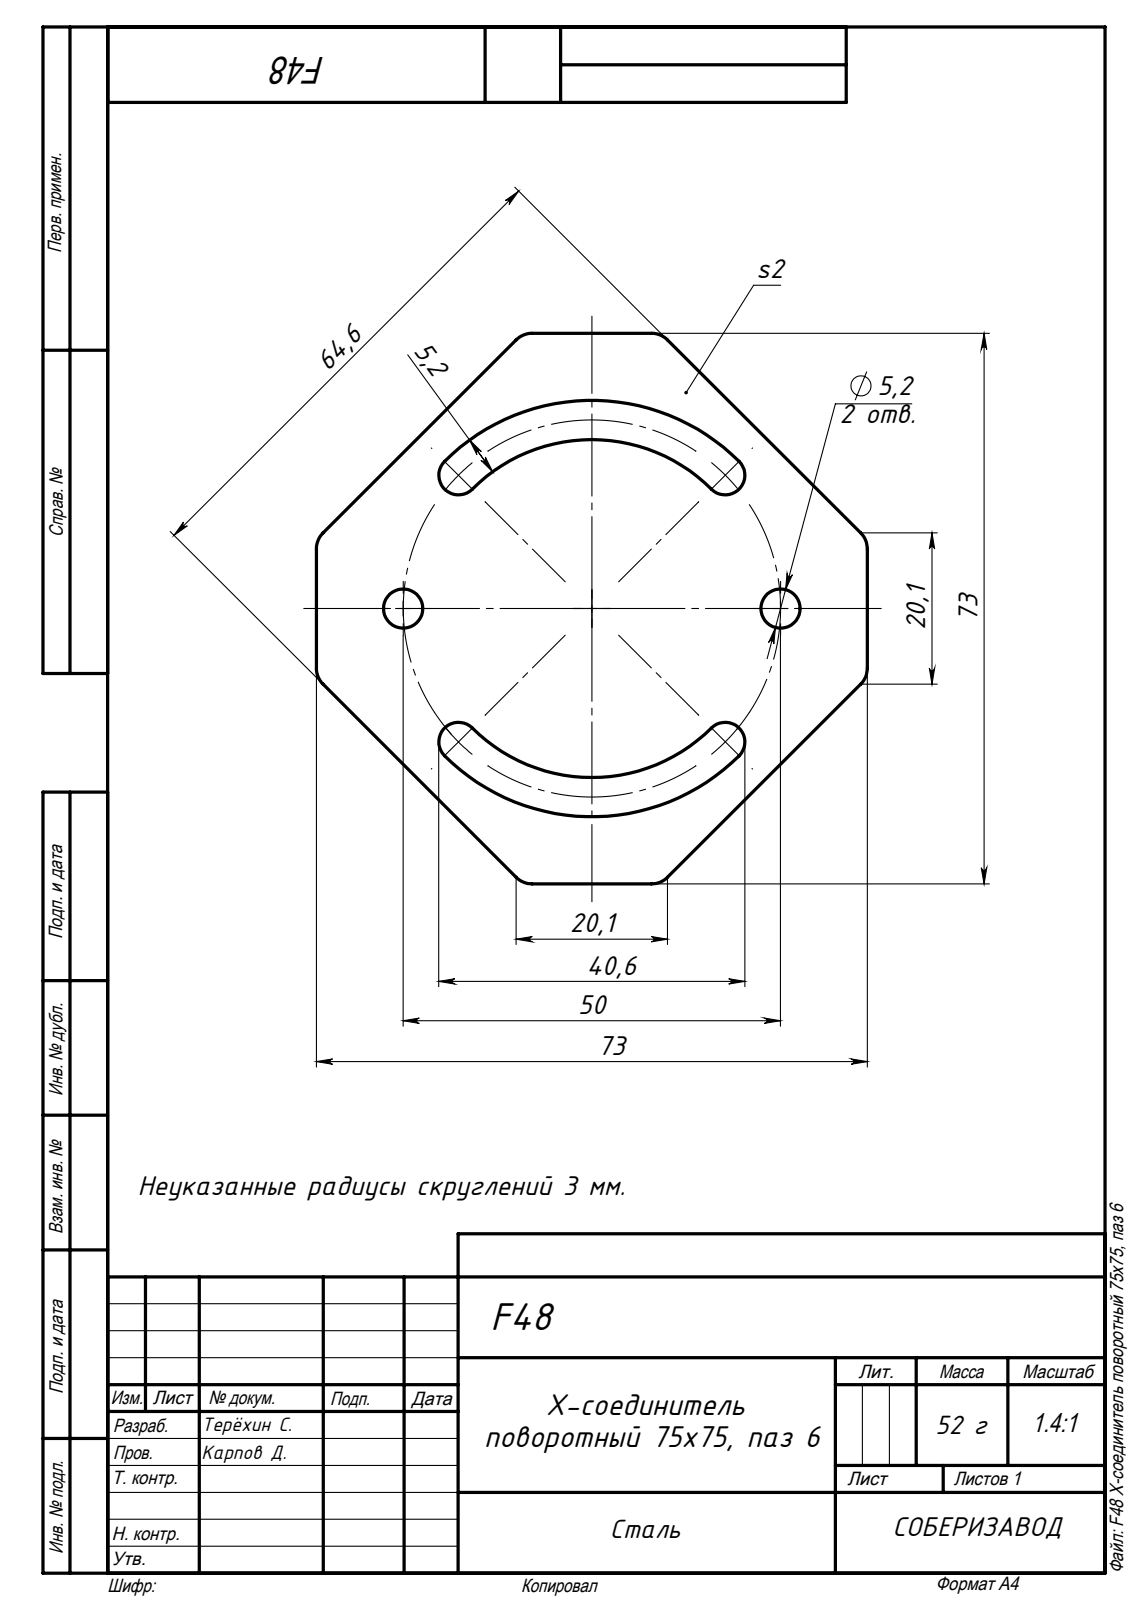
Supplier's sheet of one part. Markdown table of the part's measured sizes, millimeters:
| quantity | value |
| --- | --- |
| STEP written by | SolidWorks 2020 (AUTOMOTIVE_DESIGN) |
| units | millimeters |
| bodies | 1 solid, 32 faces (10 planar, 22 cylindrical, 0 other) |
| overall size | 73 × 73 × 2 |
| volume | 6 676 mm³ |
| surface area | 7 575 mm² |
| round holes (diameter × count) | 5.2 × 2 |
| partial cylindrical surfaces (radius × count) | 3 × 8, 2.6 × 4, 22.4 × 1, 27.6 × 1 |
| main face-to-face distances | 2, 64.54, 73 |
| hole center spacings | 50 |
